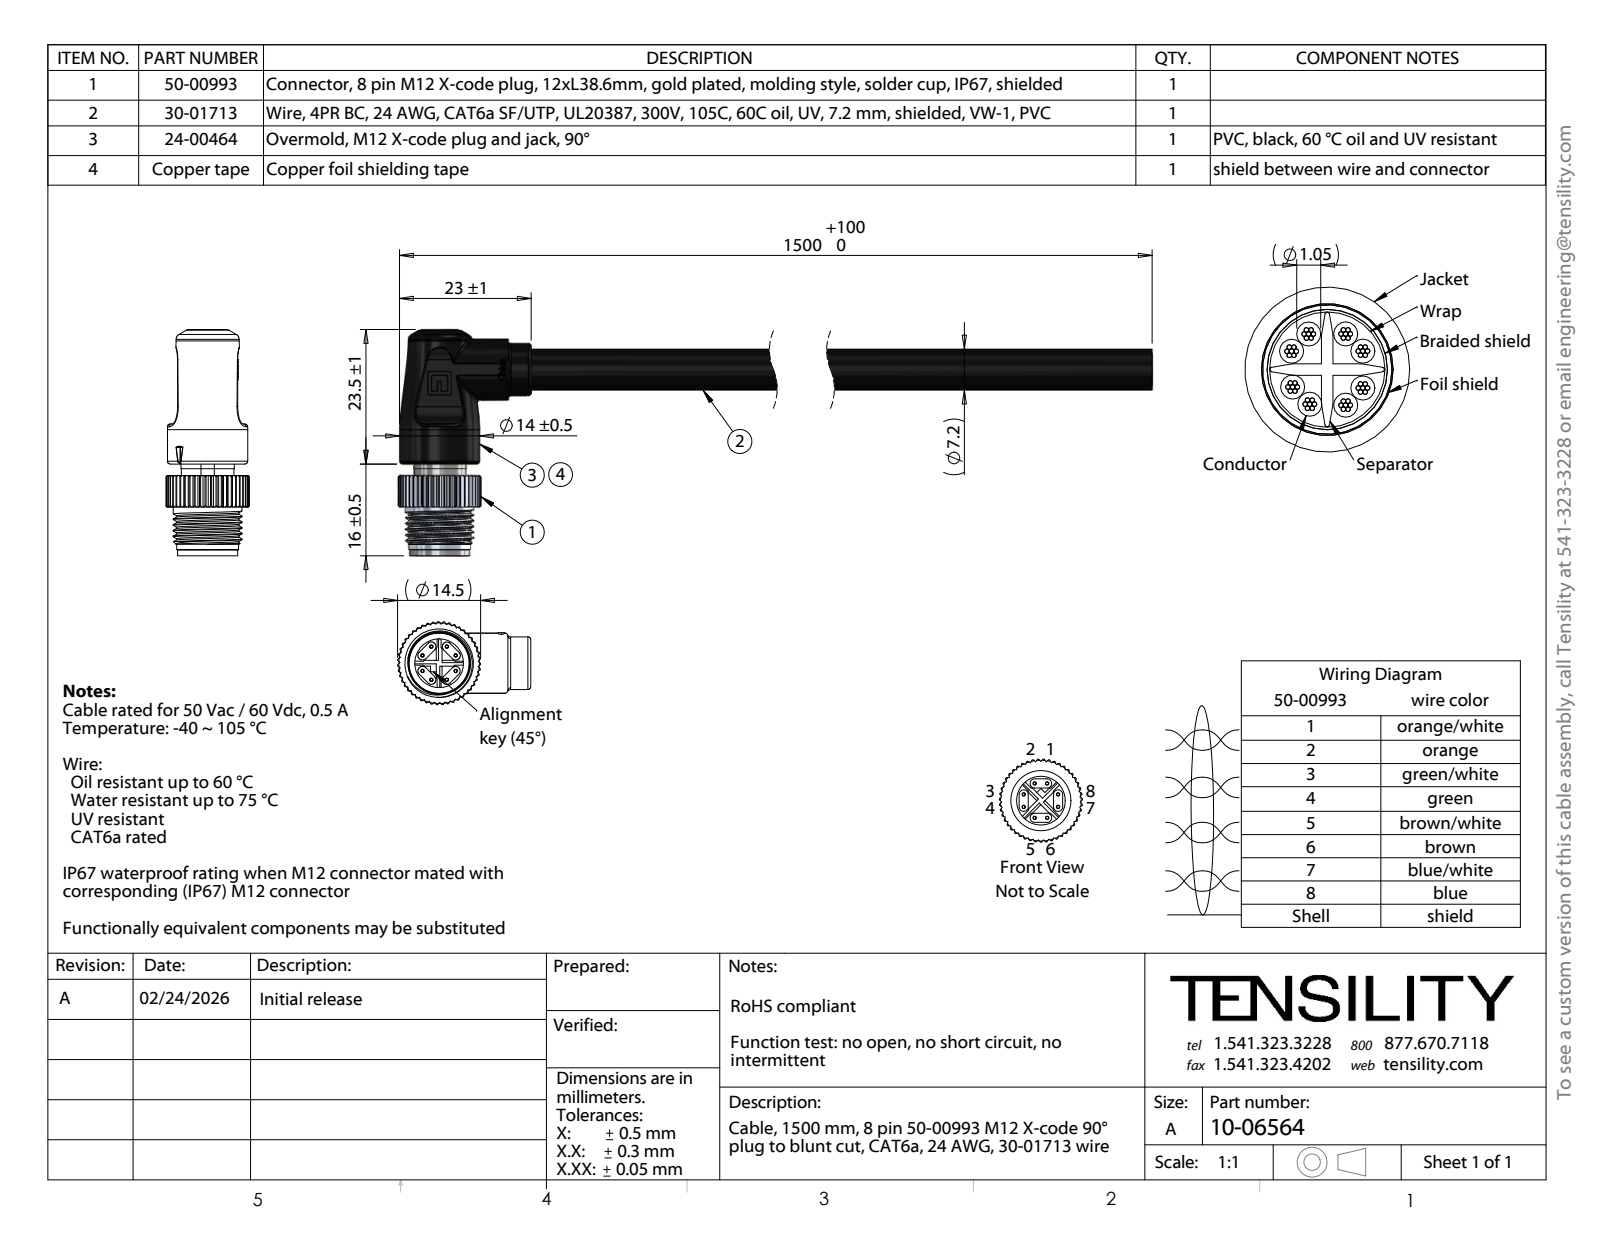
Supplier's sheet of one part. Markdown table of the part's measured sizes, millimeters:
| quantity | value |
| --- | --- |
| part name | 50-00993-03; 10-06564; 30-01713_blunt cut; 50-00993-04_默认 (+5 more) |
| STEP written by | SolidWorks 2025 (CONFIG_CONTROL_DESIGN) |
| units | millimeters |
| bodies | 85 solids, 1492 faces (552 planar, 617 cylindrical, 323 other) |
| overall size | 173.25 × 39.5 × 14.49 |
| volume | 10 489 mm³ |
| surface area | 46 188 mm² |
| round holes (diameter × count) | 0.2 × 56, 0.6 × 8, 1.2 × 8, 2 × 1, 2.5 × 1, 5.03 × 1, 5.25 × 1, 5.65 × 1, 5.75 × 1, 7.5 × 1, 8.5 × 1, 9.07 × 1 |
| round bosses / shafts (diameter × count) | 1.4 × 8, 1.15 × 8, 1.05 × 8, 0.8 × 8, 9.2 × 2, 14 × 1, 12 × 1, 11 × 1 |
| partial cylindrical surfaces (radius × count) | 0.1 × 12, 0.8 × 8, 1 × 8, 0.5 × 6, 2.17 × 4, 7.25 × 1 |
| main face-to-face distances | 0.5, 2, 0.99, 0.98, 6, 5.5, 5, 16.25, 16.75, 0.7 |
| hole center spacings | 0.35, 1.61, 1.78, 3.19, 0.41, 1.06, 1.43, 1.93 |
